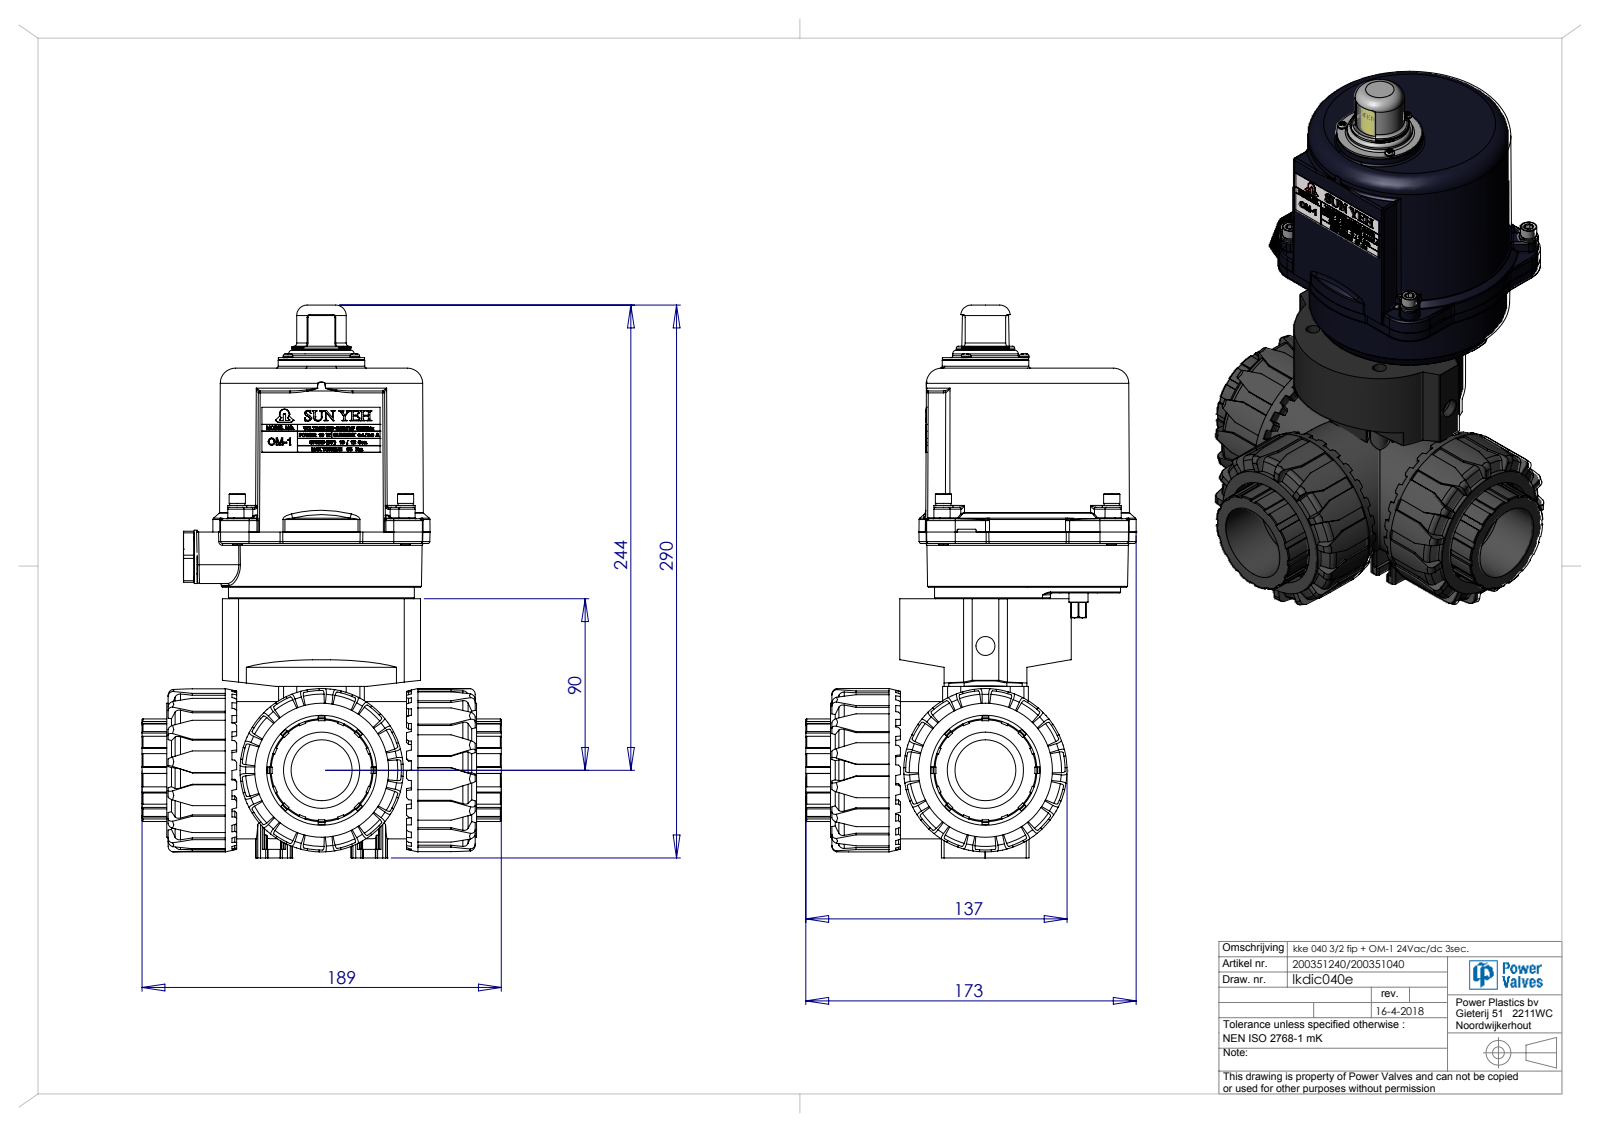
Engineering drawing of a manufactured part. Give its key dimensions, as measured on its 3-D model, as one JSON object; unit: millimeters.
{"part_name": "OM1比例式貼紙; lkdic040e_07; OM1A92(開度指示); lkdic040e (+8 more)", "step_written_by": "SolidWorks 2014 (AUTOMOTIVE_DESIGN)", "units": "millimeters", "bodies": {"solids": 29, "faces": 5615, "planar": 2562, "cylindrical": 1212, "other": 1841}, "overall_size": [290.1, 188.61, 173.44], "volume_mm3": 1397000, "surface_area_mm2": 397428, "round_holes": [[5, 8], [6.8, 6], [3.24, 4], [4.13, 4], [4.2, 4], [4.5, 4], [4.6, 4], [3.5, 3], [2.46, 2], [2.46, 2], [2.9, 2], [8, 2]], "round_bosses_or_shafts": [[5, 8], [10, 5], [8, 5], [10.39, 4], [8.5, 4], [4.4, 4], [28, 3], [3, 3]], "partial_cylinders_radius": [[1, 105], [3, 49], [0.5, 30], [0.24, 28], [3.1, 28], [1.5, 25], [0.1, 10], [1.35, 8]], "face_to_face_distances": [35, 2.5, 118.5, 83.5, 131, 13, 7.3, 121, 86, 18.4], "hole_center_spacings": [43.01, 35, 25, 30.8, 35.35, 49.5, 88.39, 10.01]}
